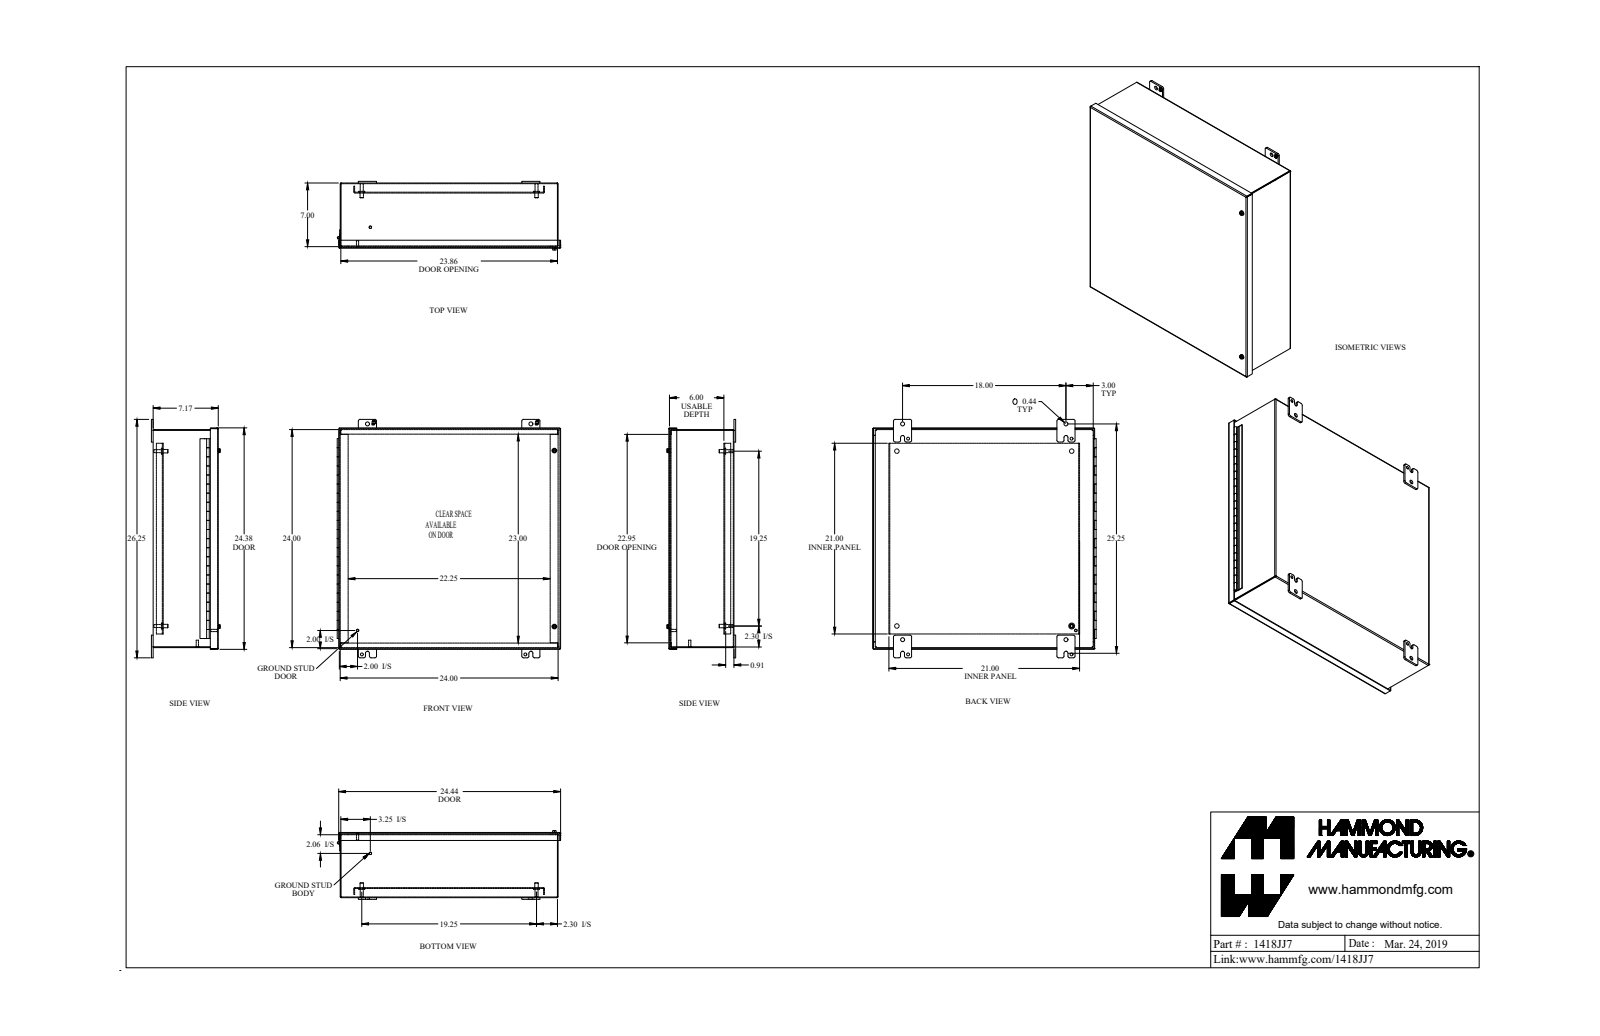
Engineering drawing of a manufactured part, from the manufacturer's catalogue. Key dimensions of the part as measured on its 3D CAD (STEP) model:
Part name (STEP PRODUCT): 1418JJ7_Default
STEP written by: SolidWorks 2018 (CONFIG_CONTROL_DESIGN)
Units: inches
Bodies: 32 solids, 942 faces (587 planar, 313 cylindrical, 42 other)
Overall size (bounding box): 26.25 × 24.604 × 7.571
Volume: 218.1 in³ · Surface area: 5 370 in²
Round holes (diameter × count): ⌀0.313 ×6, ⌀0.437 ×4, ⌀0.5 ×4, ⌀0.26 ×2, ⌀0.266 ×2, ⌀0.28 ×2, ⌀0.29 ×2, ⌀0.307 ×2, ⌀0.397 ×2, ⌀0.187 ×1, ⌀0.445 ×1, ⌀0.445 ×1
Round bosses / shafts (diameter × count): ⌀0.65 ×4, ⌀0.375 ×4, ⌀0.33 ×4, ⌀1 ×2, ⌀0.51 ×2, ⌀0.5 ×2, ⌀0.39 ×2, ⌀0.281 ×2
Partial cylindrical surfaces — rounded edges, fillets, slot ends (radius × count): R0.188 ×24, R0.25 ×20, R0.036 ×12, R0.108 ×12, R0.218 ×8, R0.133 ×6, R0.06 ×5, R0.125 ×4
Main face-to-face distances: 0.072, 7.1, 23.928, 7.172, 7.028, 0.095, 5.996, 6.091, 1.104, 1.032
Hole centre spacings: 19.25, 18, 13.612, 22.259, 0.059, 1.625, 1.735, 1.736
